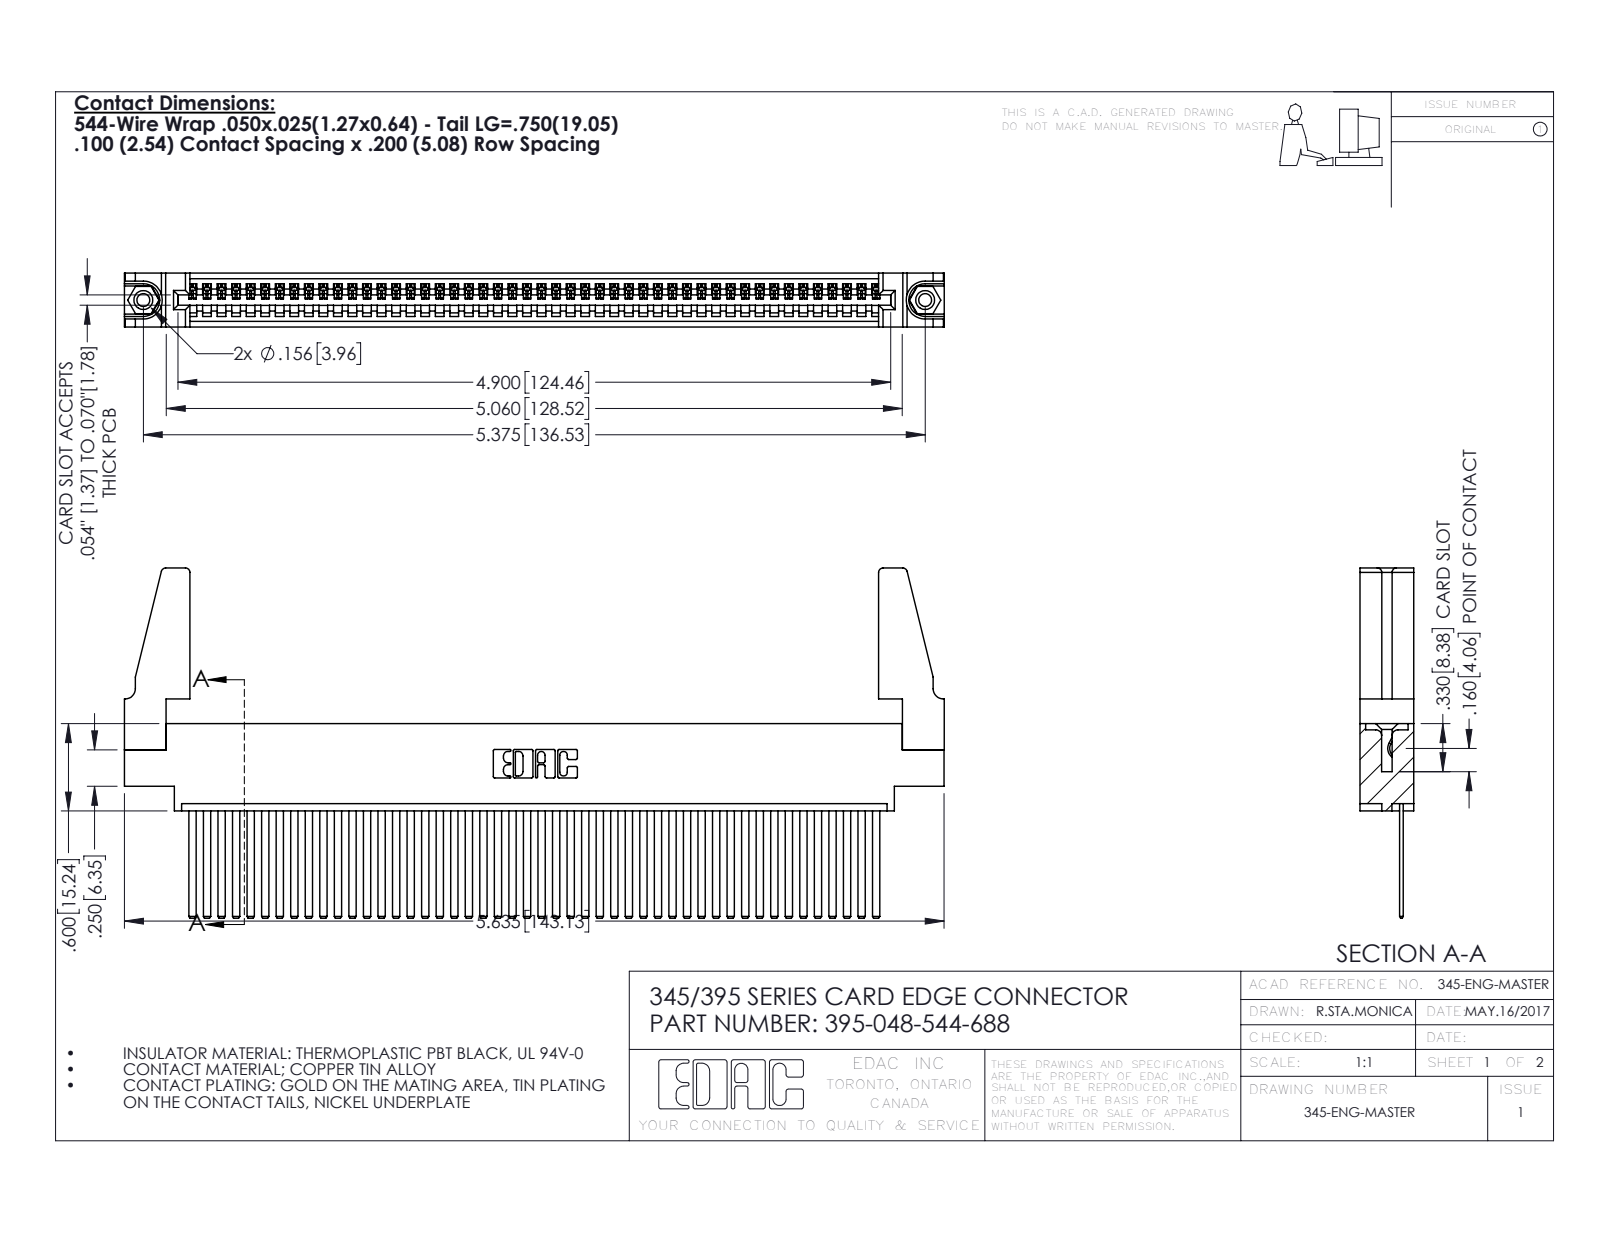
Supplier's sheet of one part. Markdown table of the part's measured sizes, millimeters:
| quantity | value |
| --- | --- |
| part name | 345-250-001_345-250-001-102; 345-292-001_345-293-144; 345 Part_0.170 Offset - 0.156 Dia-TH; 345-220-078_345-220-088 (+1 more) |
| STEP written by | SolidWorks 2016 (CONFIG_CONTROL_DESIGN) |
| units | millimeters |
| bodies | 53 solids, 2750 faces (1884 planar, 850 cylindrical, 16 other) |
| overall size | 143.2 × 61.1 × 9.4 |
| volume | 17 340 mm³ |
| surface area | 23 730 mm² |
| round holes (diameter × count) | 2.3 × 2, 3.2 × 2, 4 × 2, 1.6 × 1 |
| round bosses / shafts (diameter × count) | 3.9 × 2 |
| partial cylindrical surfaces (radius × count) | 0.2 × 96, 0.3 × 22, 0.8 × 8, 0.2 × 6, 0.8 × 6, 0.7 × 3, 0.8 × 2, 1 × 2 |
| main face-to-face distances | 1.8, 7.6, 2.5, 6.9, 0.6, 9.4, 5.1, 5.7, 4.4, 3.8 |
| hole center spacings | 6.9, 130.5, 136.5 |
